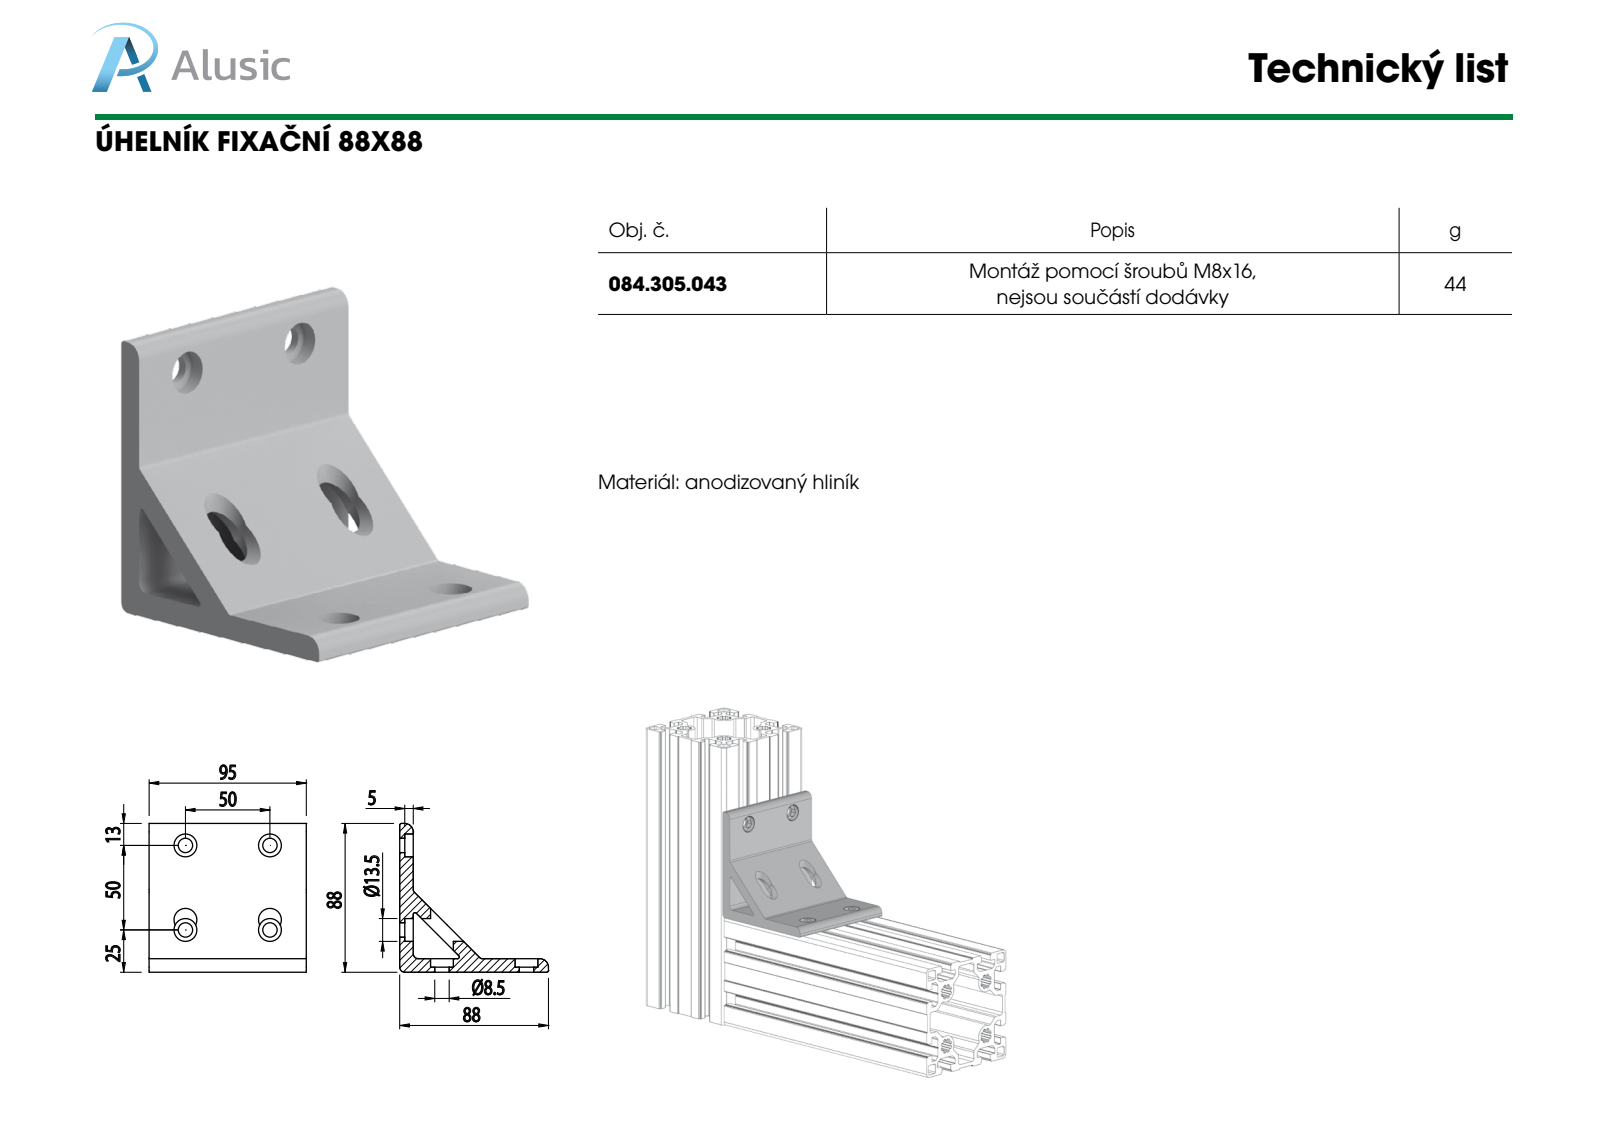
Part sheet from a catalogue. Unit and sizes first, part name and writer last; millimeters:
Units: millimetres
Overall size (bounding box): 93 × 88 × 88
Round holes (diameter × count): ⌀8.5 ×8, ⌀13.5 ×8
Partial cylindrical surfaces — rounded edges, fillets, slot ends (radius × count): R1 ×4, R2 ×2, R3 ×2, R5 ×2
Main face-to-face distances: 8, 93, 3, 5, 88, 85, 80
Hole centre spacings: 50, 70.71
Volume: 149 150 mm³ · Surface area: 43 207 mm²
Bodies: 1 solid, 54 faces (20 planar, 34 cylindrical, 0 other)
Part name (STEP PRODUCT): 084.305.043
STEP written by: SolidWorks 2012 (AUTOMOTIVE_DESIGN)
